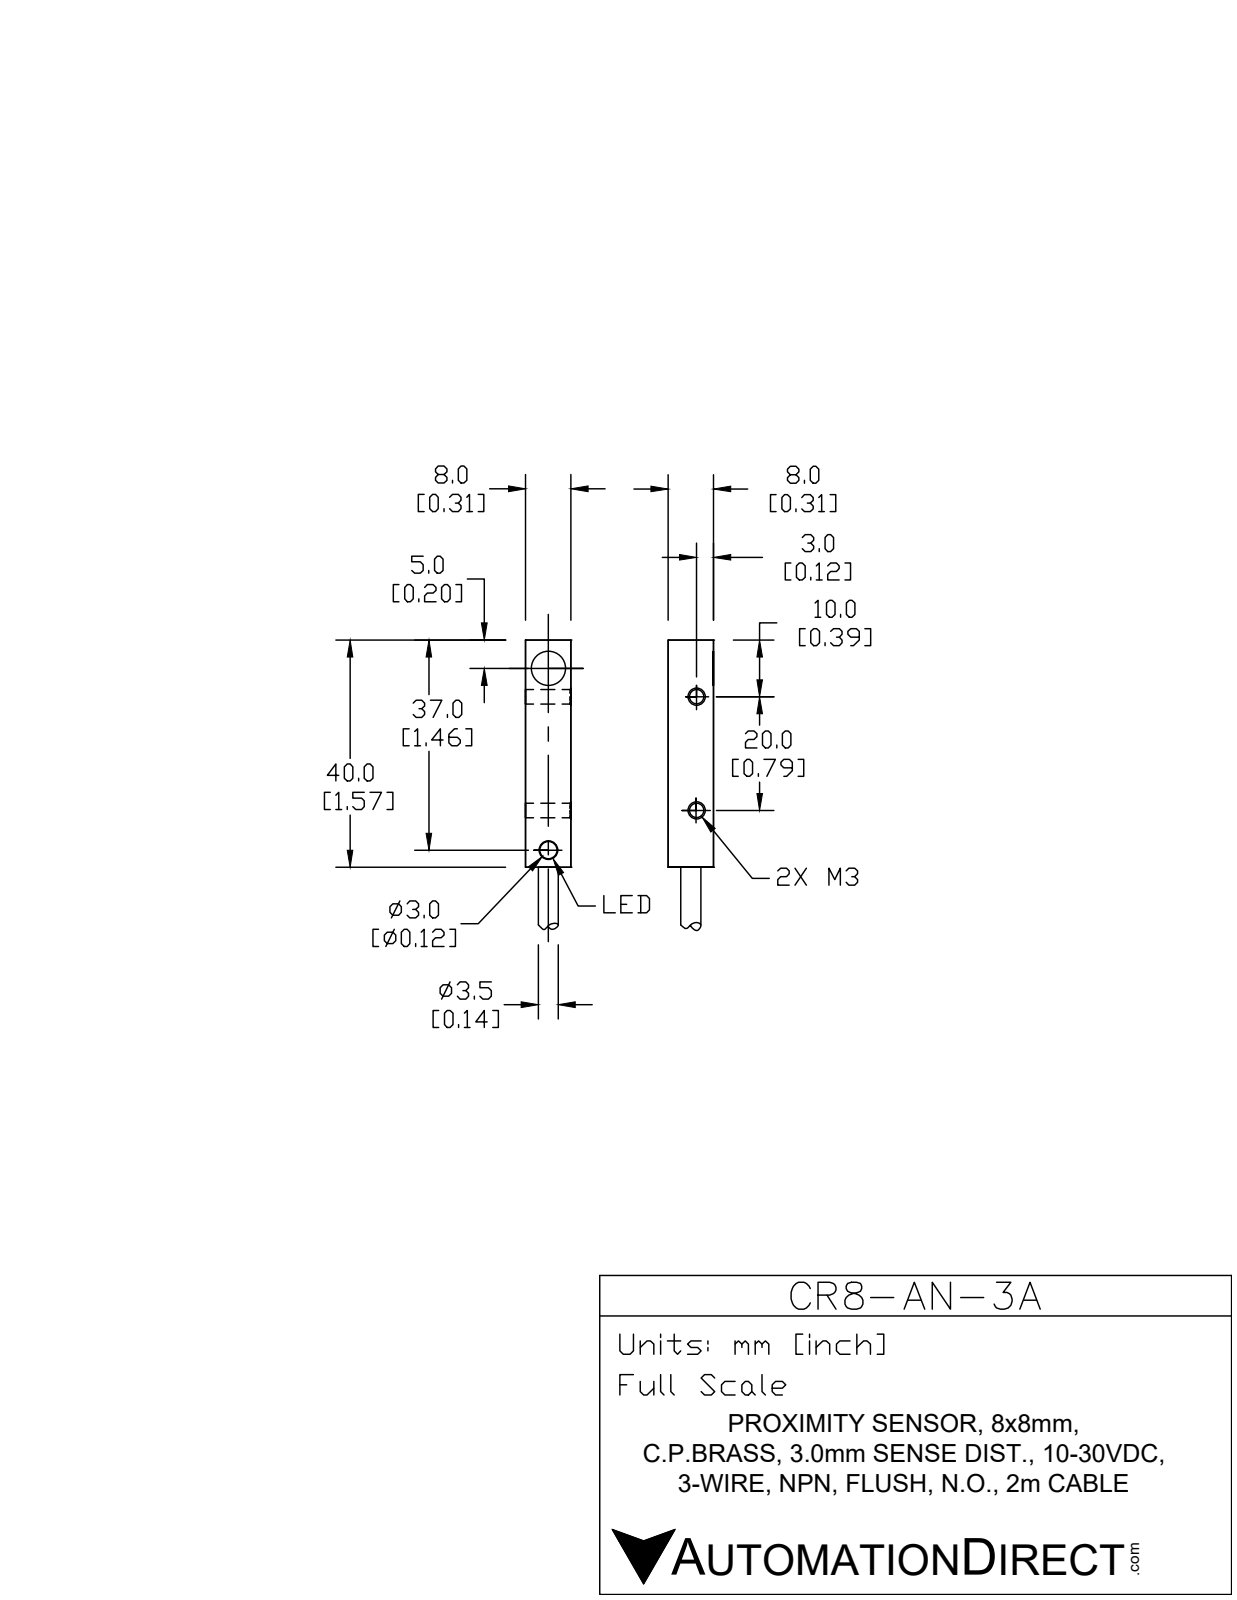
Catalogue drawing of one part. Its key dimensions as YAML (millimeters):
part_name: "CR8-AN-2A"
step_written_by: "SolidWorks 2021 (AUTOMOTIVE_DESIGN)"
units: millimeters
bodies: {solids: 1, faces: 21, planar: 9, cylindrical: 5, other: 7}
overall_size: [61.9, 8, 8]
volume: 2690
surface_area: 1761
round_holes:
  - {diameter: 2.5, count: 2}
  - {diameter: 6.9, count: 1}
round_bosses_or_shafts:
  - {diameter: 6.8, count: 1}
  - {diameter: 3.5, count: 1}
face_to_face_distances: [8, 40, 7.9, 7.7, 7.6]
hole_center_spacings: [20]
